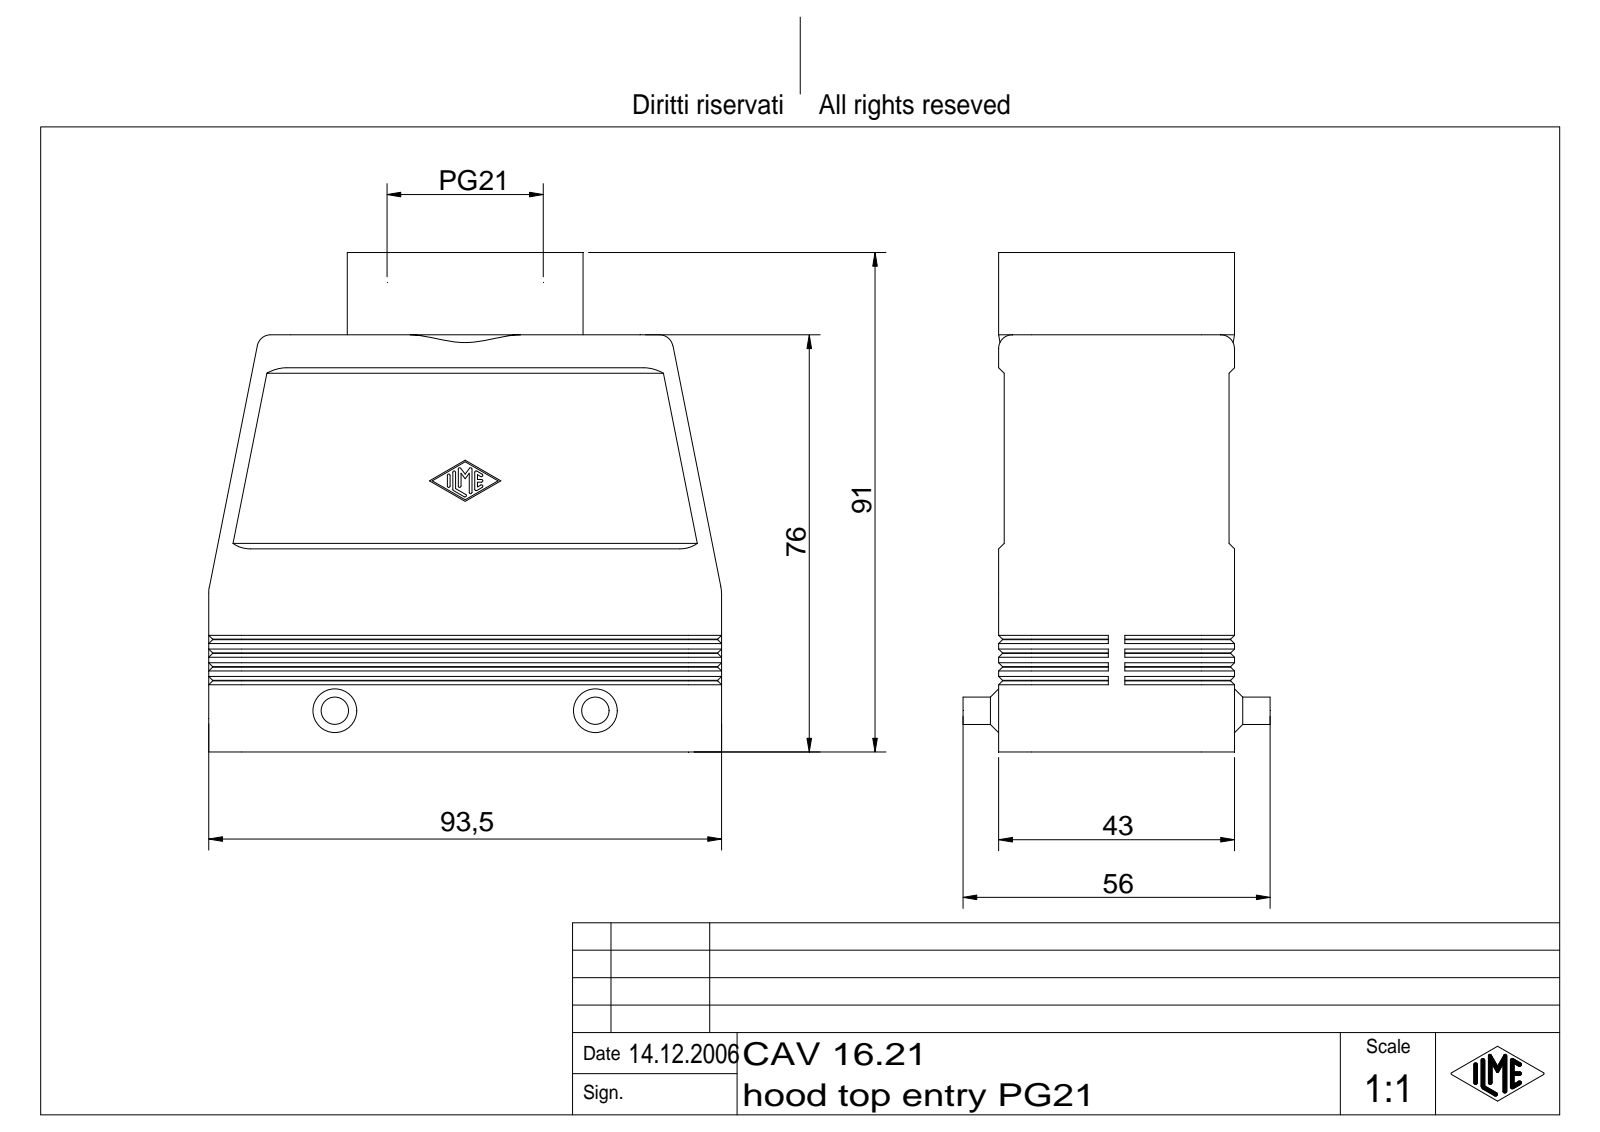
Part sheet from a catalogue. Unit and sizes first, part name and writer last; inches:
Units: inches
Overall size (bounding box): 3.681 × 3.583 × 2.205
Round holes (diameter × count): ⌀0.976 ×1, ⌀1.054 ×1
Round bosses / shafts (diameter × count): ⌀0.197 ×2, ⌀1.693 ×1, ⌀1.015 ×1
Partial cylindrical surfaces — rounded edges, fillets, slot ends (radius × count): R0.01 ×14, R0.236 ×10, R0.079 ×4, R0.098 ×4, R0.118 ×4, R0.209 ×2
Main face-to-face distances: 0.118, 1.575, 1.457, 0.039, 0.079, 1.654, 1.535, 1.693, 1.614, 0.482
Volume: 5.179 in³ · Surface area: 72.72 in²
Bodies: 1 solid, 413 faces (153 planar, 108 cylindrical, 152 other)
Part name (STEP PRODUCT): CAO Tüllengehäuse 2 Bügel für einen Einsatz
STEP written by: Autodesk Inventor 7 (AUTOMOTIVE_DESIGN)
